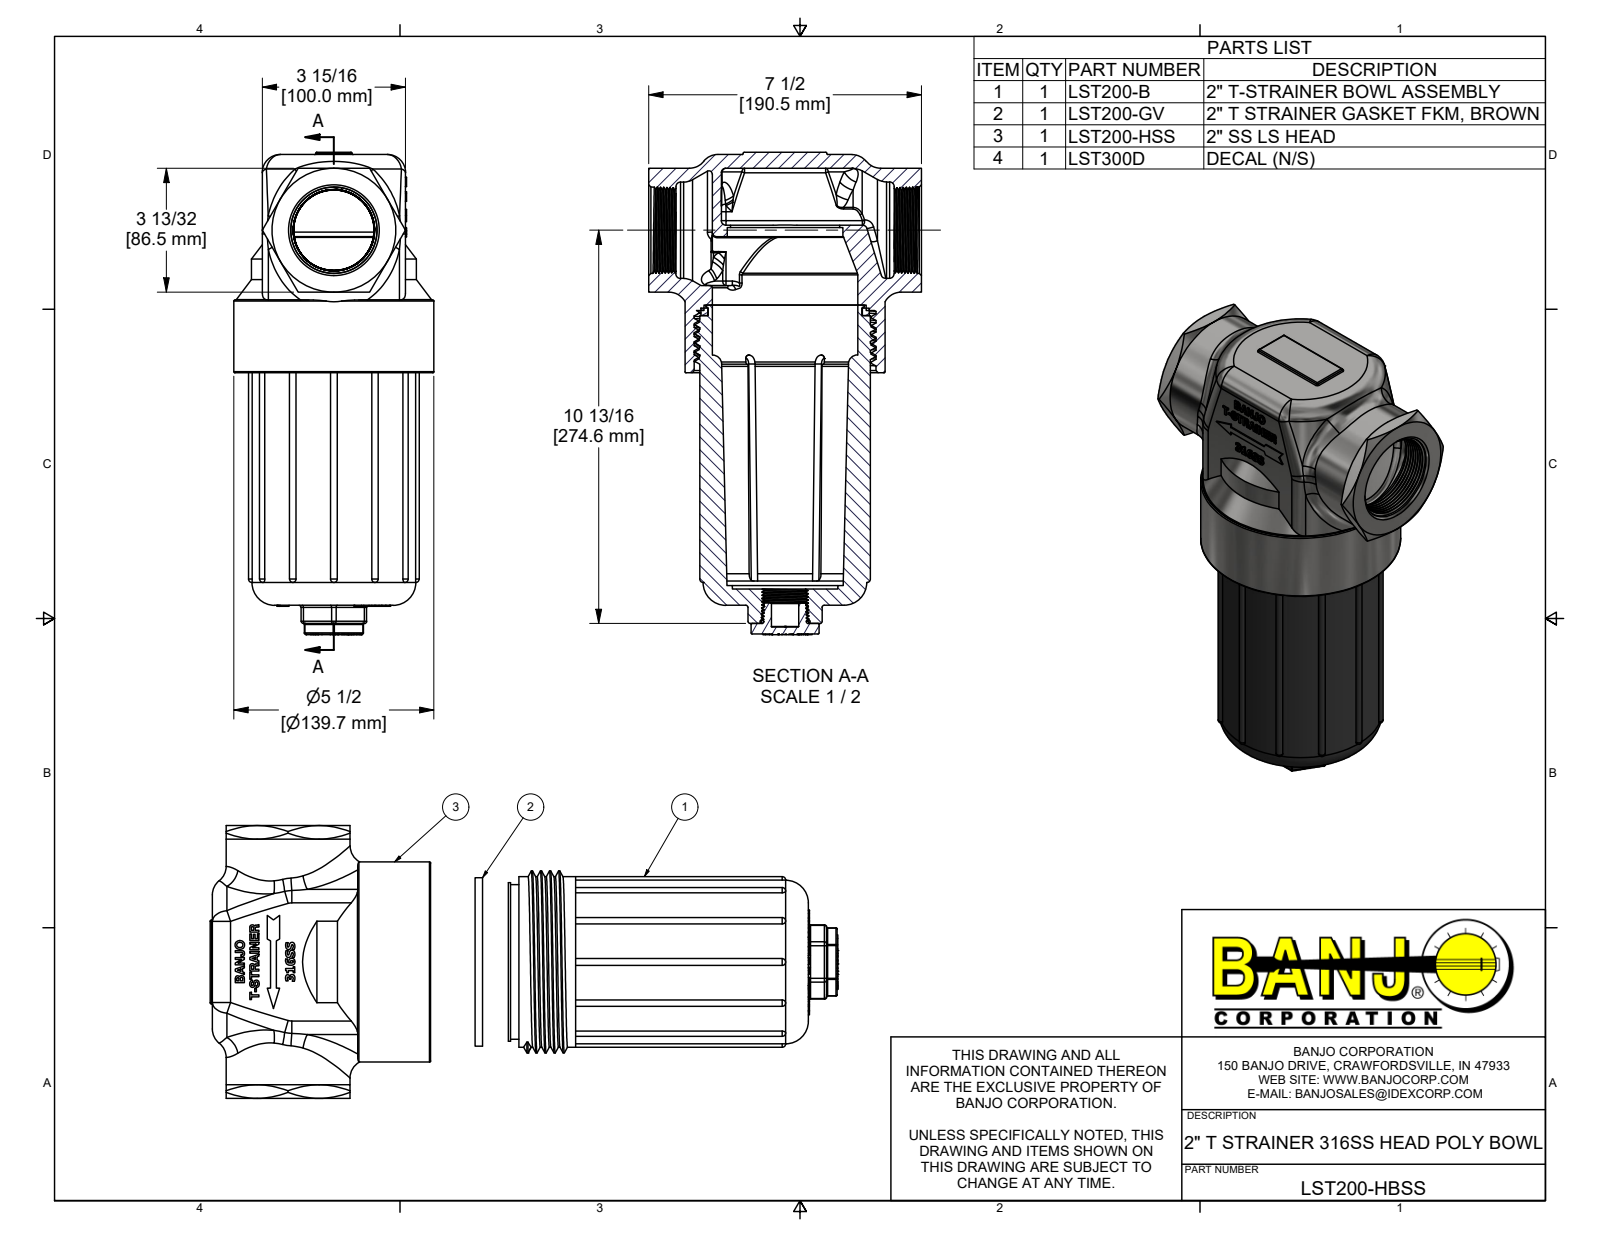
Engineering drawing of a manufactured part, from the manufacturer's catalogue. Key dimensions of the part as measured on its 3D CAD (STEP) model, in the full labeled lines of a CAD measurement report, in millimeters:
Part name (STEP PRODUCT): LST200-HBSS; LST200-HSS; LST200B; LST200XB (+3 more)
STEP written by: Autodesk Inventor 2019 (AUTOMOTIVE_DESIGN)
Units: millimetres
Bodies: 5 solids, 1651 faces (711 planar, 158 cylindrical, 782 other)
Overall size (bounding box): 544 × 190.5 × 139.7
Volume: 1 662 000 mm³ · Surface area: 492 100 mm²
Round holes (diameter × count): ⌀19.1 ×1, ⌀67.2 ×1, ⌀73.7 ×1, ⌀76.2 ×1, ⌀80.8 ×1, ⌀81.3 ×1, ⌀101.6 ×1, ⌀107.3 ×1, ⌀113.2 ×1, ⌀120.1 ×1, ⌀127 ×1
Round bosses / shafts (diameter × count): ⌀139.7 ×1, ⌀119.2 ×1, ⌀117.6 ×1, ⌀114.3 ×1, ⌀110.7 ×1, ⌀108 ×1, ⌀86.5 ×1, ⌀33.4 ×1
Partial cylindrical surfaces — rounded edges, fillets, slot ends (radius × count): R0.8 ×28, R2.4 ×21, R3.2 ×21, R1.5 ×12, R12.7 ×8, R2.3 ×2, R3 ×2, R9.9 ×1
Main face-to-face distances: 9.7, 90.3, 9.7, 100, 102.8, 112.4, 190.9, 293.7, 303.3, 7.4
